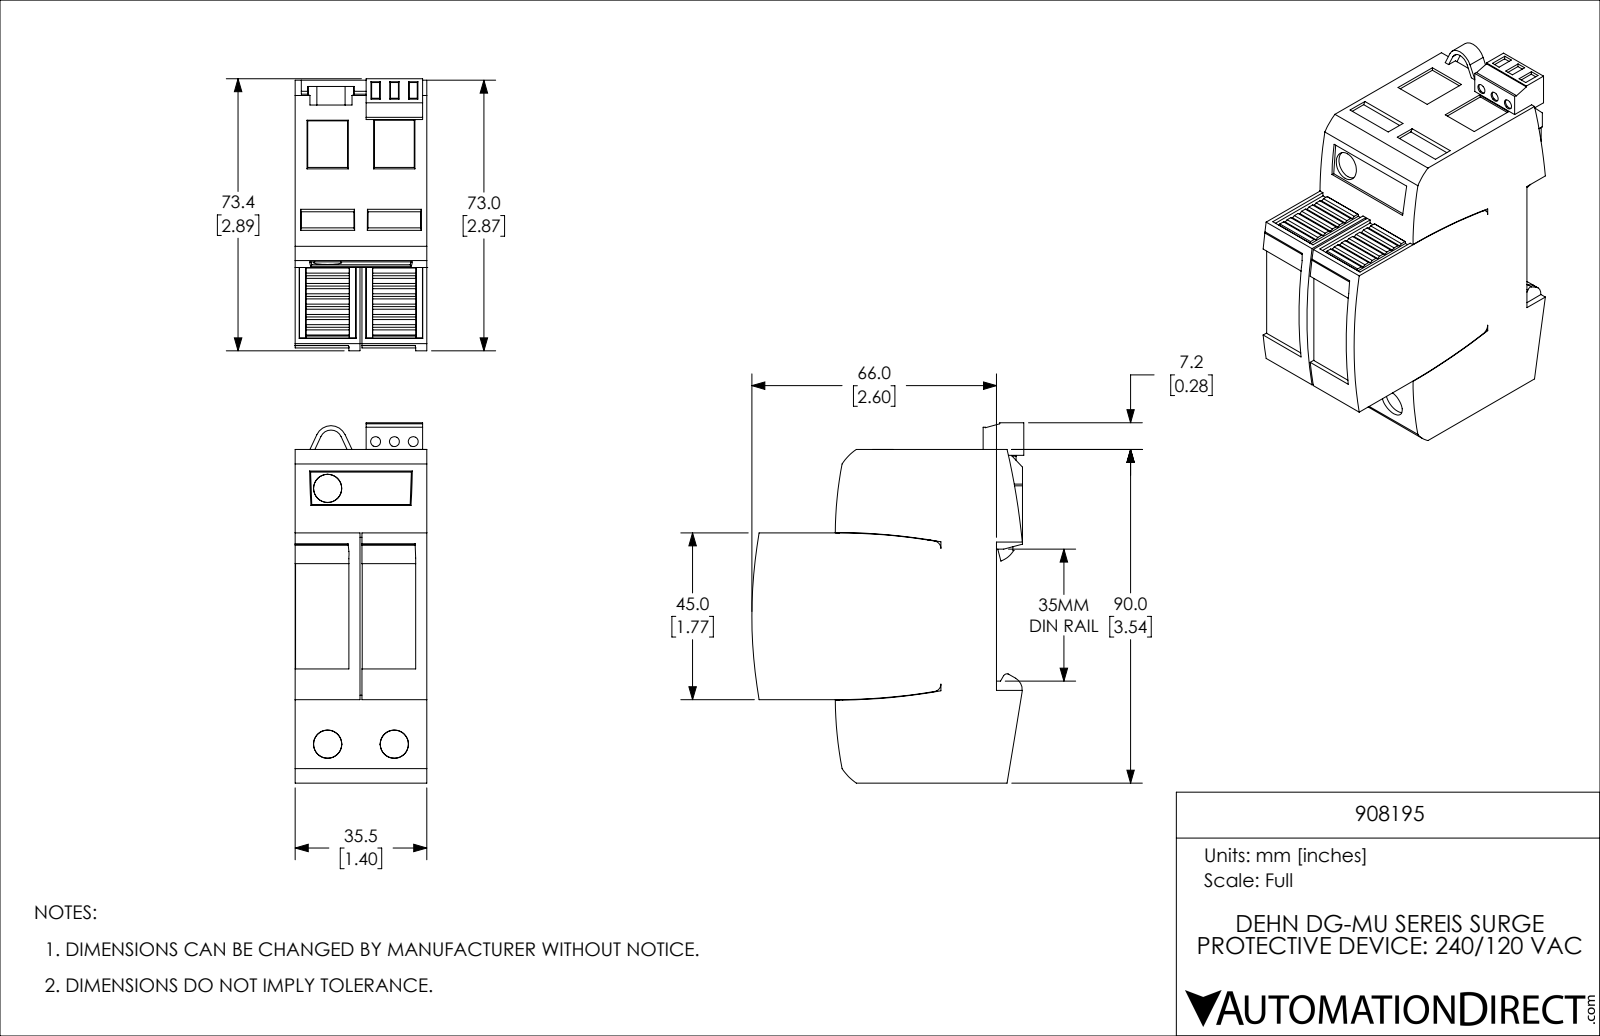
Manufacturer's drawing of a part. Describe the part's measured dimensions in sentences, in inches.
The part is named "908195". Its 3-D file was written by "SolidWorks 2019 (CONFIG_CONTROL_DESIGN)". It is 1 solid with 516 faces: 392 planar, 96 cylindrical and 28 other. Overall it measures 3.827 by 2.89 by 1.398 inches. Its volume is 11.01 cubic inches and its surface area 42.31 square inches. Round holes: 3 of diameter 0.106. Partial cylindrical surfaces (rounded edges, fillets, slot ends): 8 of radius 0.004, 8 of radius 0.047, 3 of radius 0.008, 3 of radius 0.02, 2 of radius 0.016, 2 of radius 0.03, 2 of radius 0.031, 2 of radius 0.079. The main face-to-face distances are 1.398, 0.709, 0.689, 0.685, 1.394, 2.518, 0.02, 0.276, 2.794, 0.024. The hole center spacings are 0.2, 0.2, 0.4.
